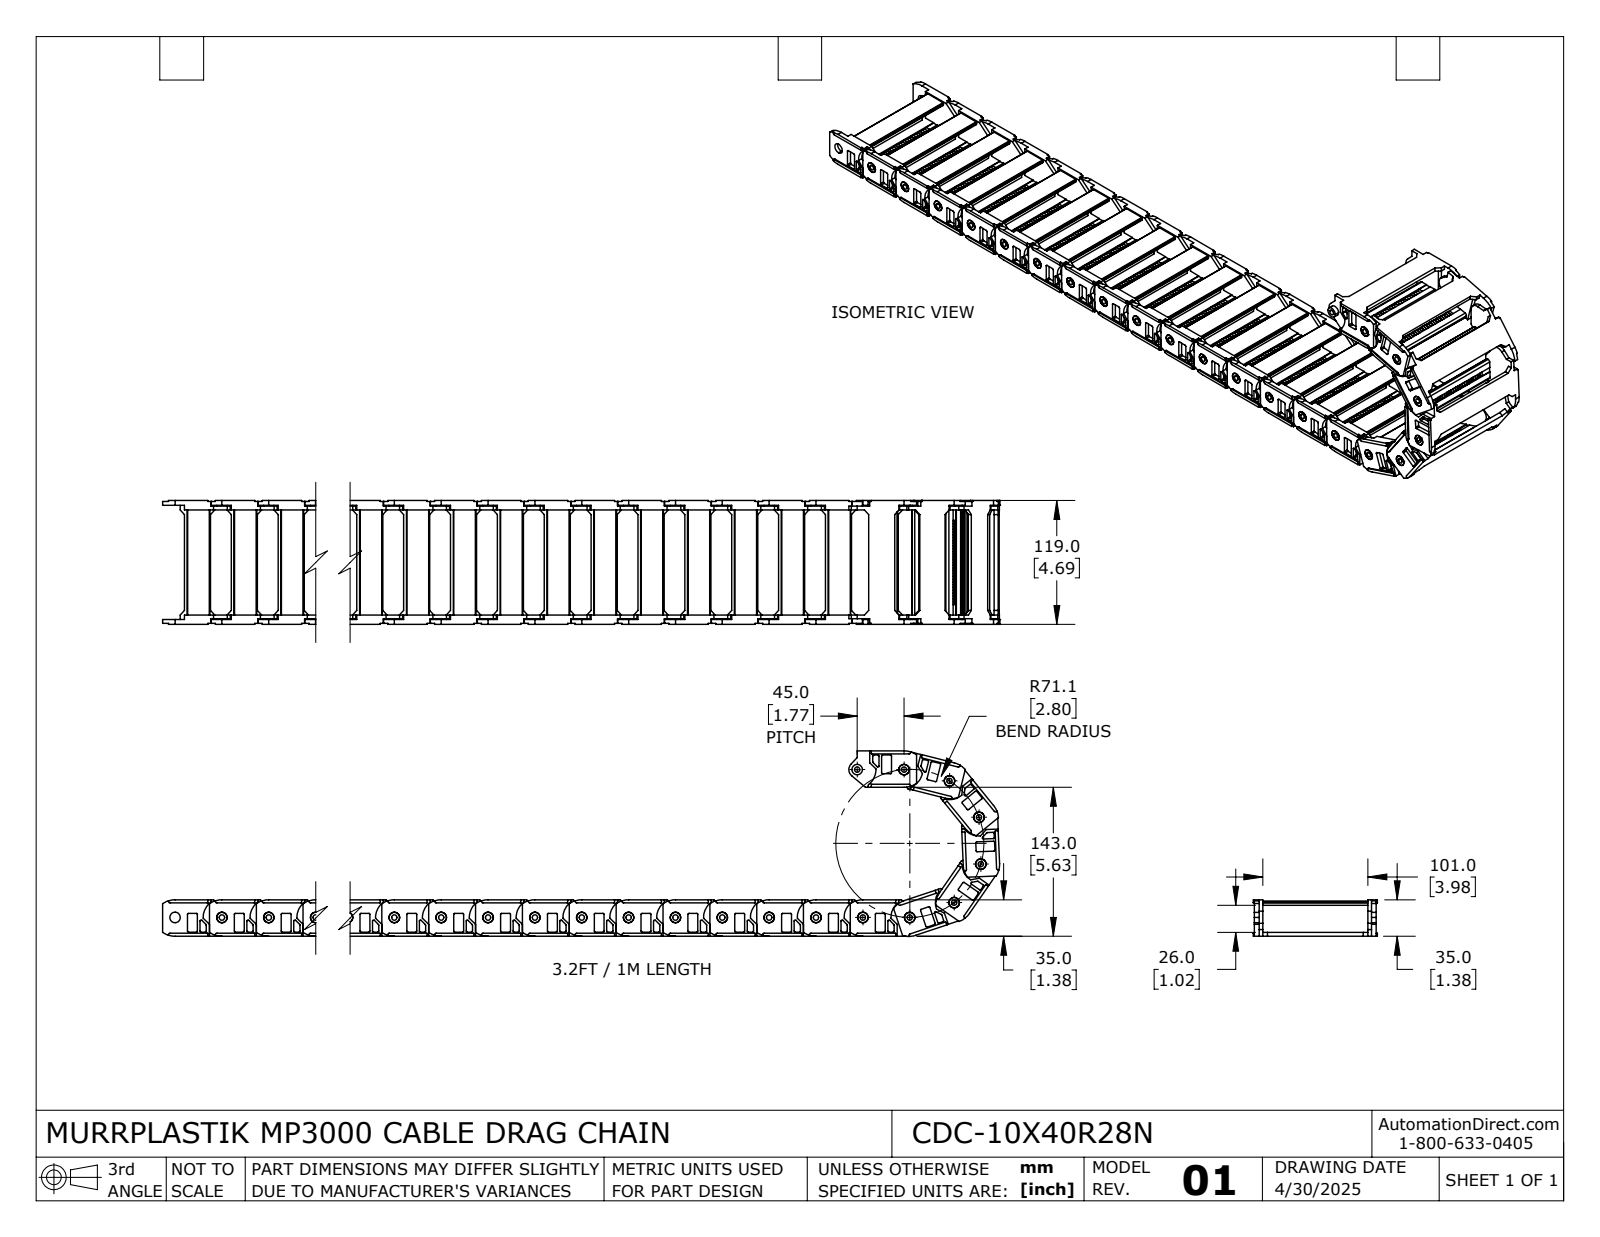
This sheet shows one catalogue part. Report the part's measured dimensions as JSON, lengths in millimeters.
{"part_name": "CDC-10X40R28N", "step_written_by": "SolidWorks 2024 (AUTOMOTIVE_DESIGN)", "units": "millimeters", "bodies": {"solids": 22, "faces": 5456, "planar": 4356, "cylindrical": 1100, "other": 0}, "overall_size": [818.28, 178.14, 119], "volume_mm3": 824420, "surface_area_mm2": 512256, "round_holes": [[5.1, 22], [10.1, 22]], "round_bosses_or_shafts": [[10, 22]], "partial_cylinders_radius": [[1, 176], [0.5, 88], [1.5, 44], [2, 44], [21, 44], [2.8, 22], [8, 22], [18, 22]], "face_to_face_distances": [4, 109, 8, 3.8, 30, 33.8, 3.7, 113.3, 4.3, 105.3], "hole_center_spacings": [45, 90, 135, 180, 225, 270, 315, 360]}
